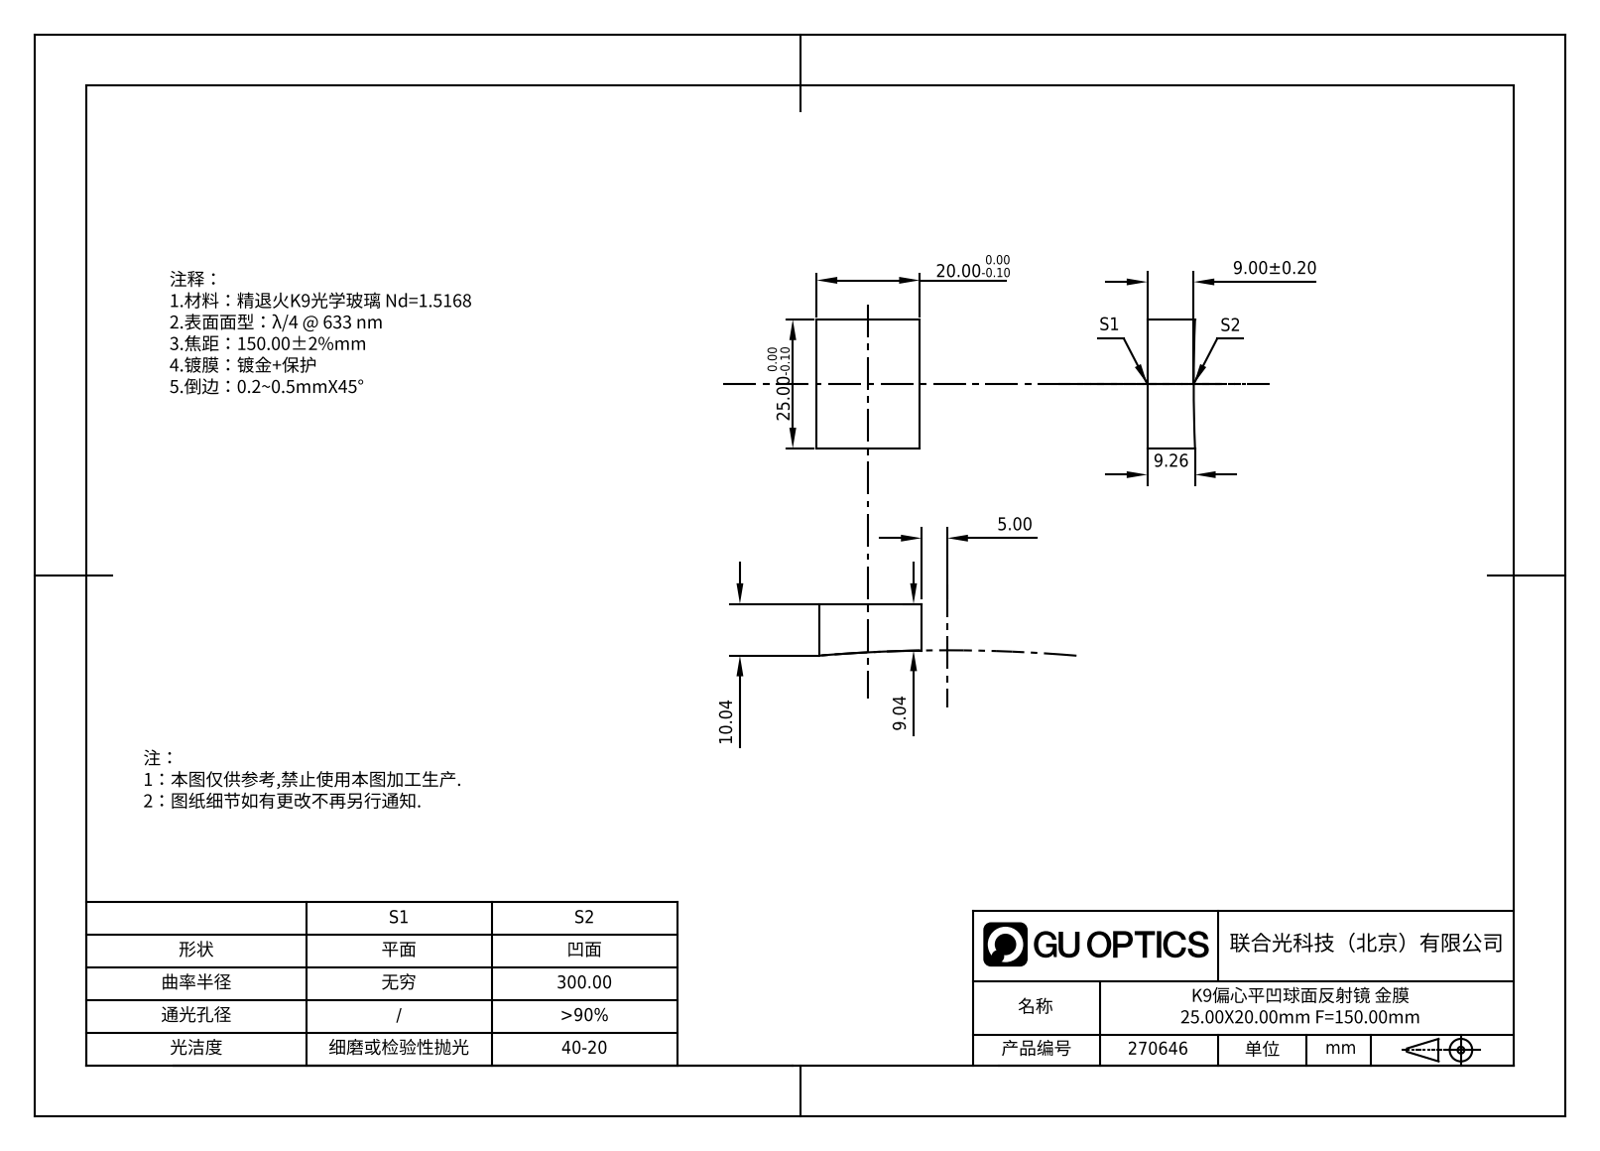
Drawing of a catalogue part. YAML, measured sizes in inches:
part_name: "270646"
step_written_by: "SolidWorks 2020 (CONFIG_CONTROL_DESIGN)"
units: inches
bodies: {solids: 1, faces: 7, planar: 5, cylindrical: 0, other: 2}
overall_size: [0.984, 0.787, 0.406]
volume: 0.29
surface_area: 2.899
face_to_face_distances: [0.787, 0.984]
